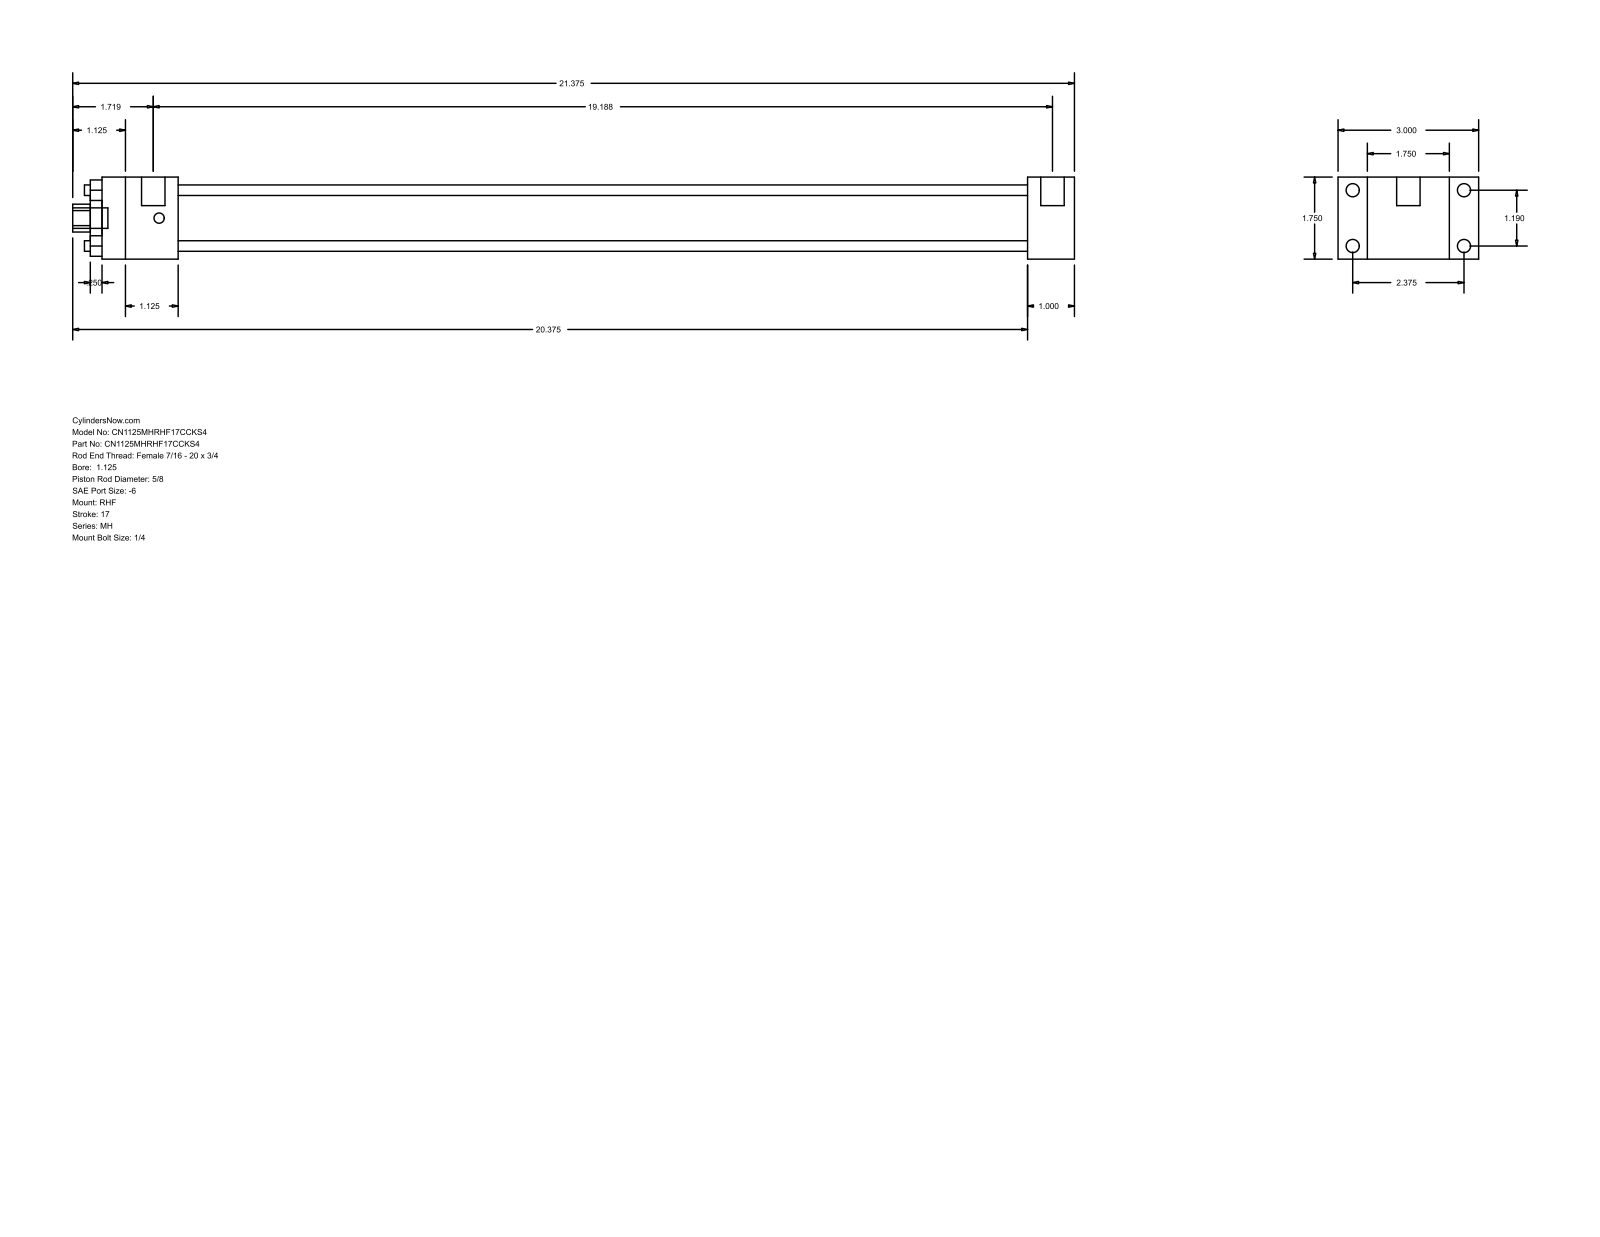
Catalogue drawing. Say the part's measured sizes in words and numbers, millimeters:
The part is named "MH_RHF__0112_0.625". Its 3-D file was written by "GSSL Pune (CONFIG_CONTROL_DESIGN)". It is 0 solids with 88 faces: 60 planar, 28 cylindrical and 0 other. Overall it measures 542.92 by 76.2 by 44.45 millimeters. Round holes: 4 of diameter 5.71, 1 of diameter 15.88, 1 of diameter 28.57, 1 of diameter 34.92. Round bosses or shafts: 4 of diameter 7.14, 4 of diameter 5.56, 2 of diameter 12.7, 1 of diameter 11.11. Partial cylindrical surfaces (rounded edges, fillets, slot ends): 1 of radius 7.54. The main face-to-face distances are 44.46, 15.87, 60.33, 25.4, 76.2, 460.37, 485.77, 41.27, 501.64, 527.04. The hole center spacings are 21.37, 30.22, 42.74.
